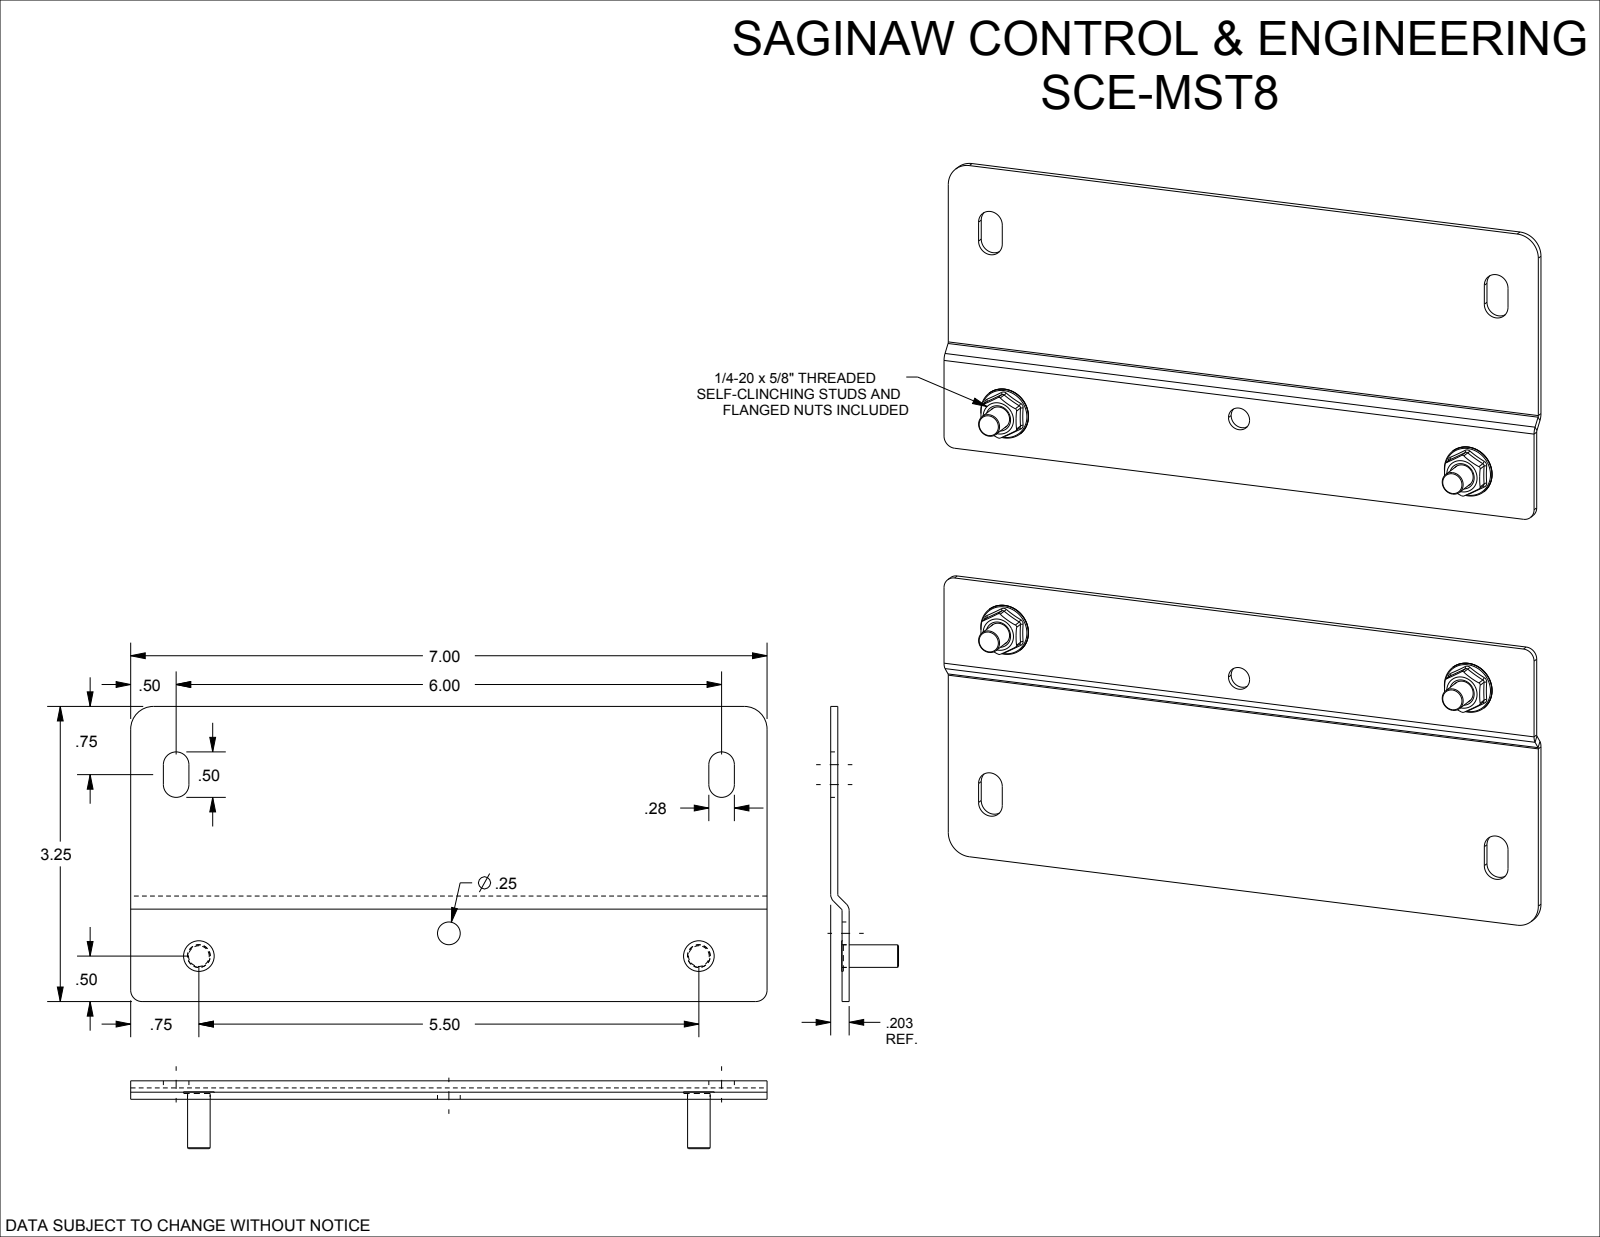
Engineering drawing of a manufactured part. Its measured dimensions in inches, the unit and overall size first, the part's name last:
Units: inches
Overall size (bounding box): 7.99 × 7 × 0.746
Round holes (diameter × count): ⌀0.25 ×6, ⌀0.25 ×4
Round bosses / shafts (diameter × count): ⌀0.563 ×4, ⌀0.337 ×4, ⌀0.248 ×4
Partial cylindrical surfaces — rounded edges, fillets, slot ends (radius × count): R0.029 ×24, R0.141 ×8, R0.023 ×4, R0.101 ×4, R0.125 ×4, R0.25 ×4
Main face-to-face distances: 0.078, 0.078, 0.125, 0.203, 0.047, 0.125, 3.245, 4.745, 1.5, 7.99
Hole centre spacings: 2.761, 3.889, 2.5, 5.5, 6.041, 3
Volume: 3.735 in³ · Surface area: 100 in²
Bodies: 10 solids, 1010 faces (332 planar, 70 cylindrical, 608 other)
Part name (STEP PRODUCT): SCE-MST8
STEP written by: SolidWorks 2019 (AUTOMOTIVE_DESIGN)
